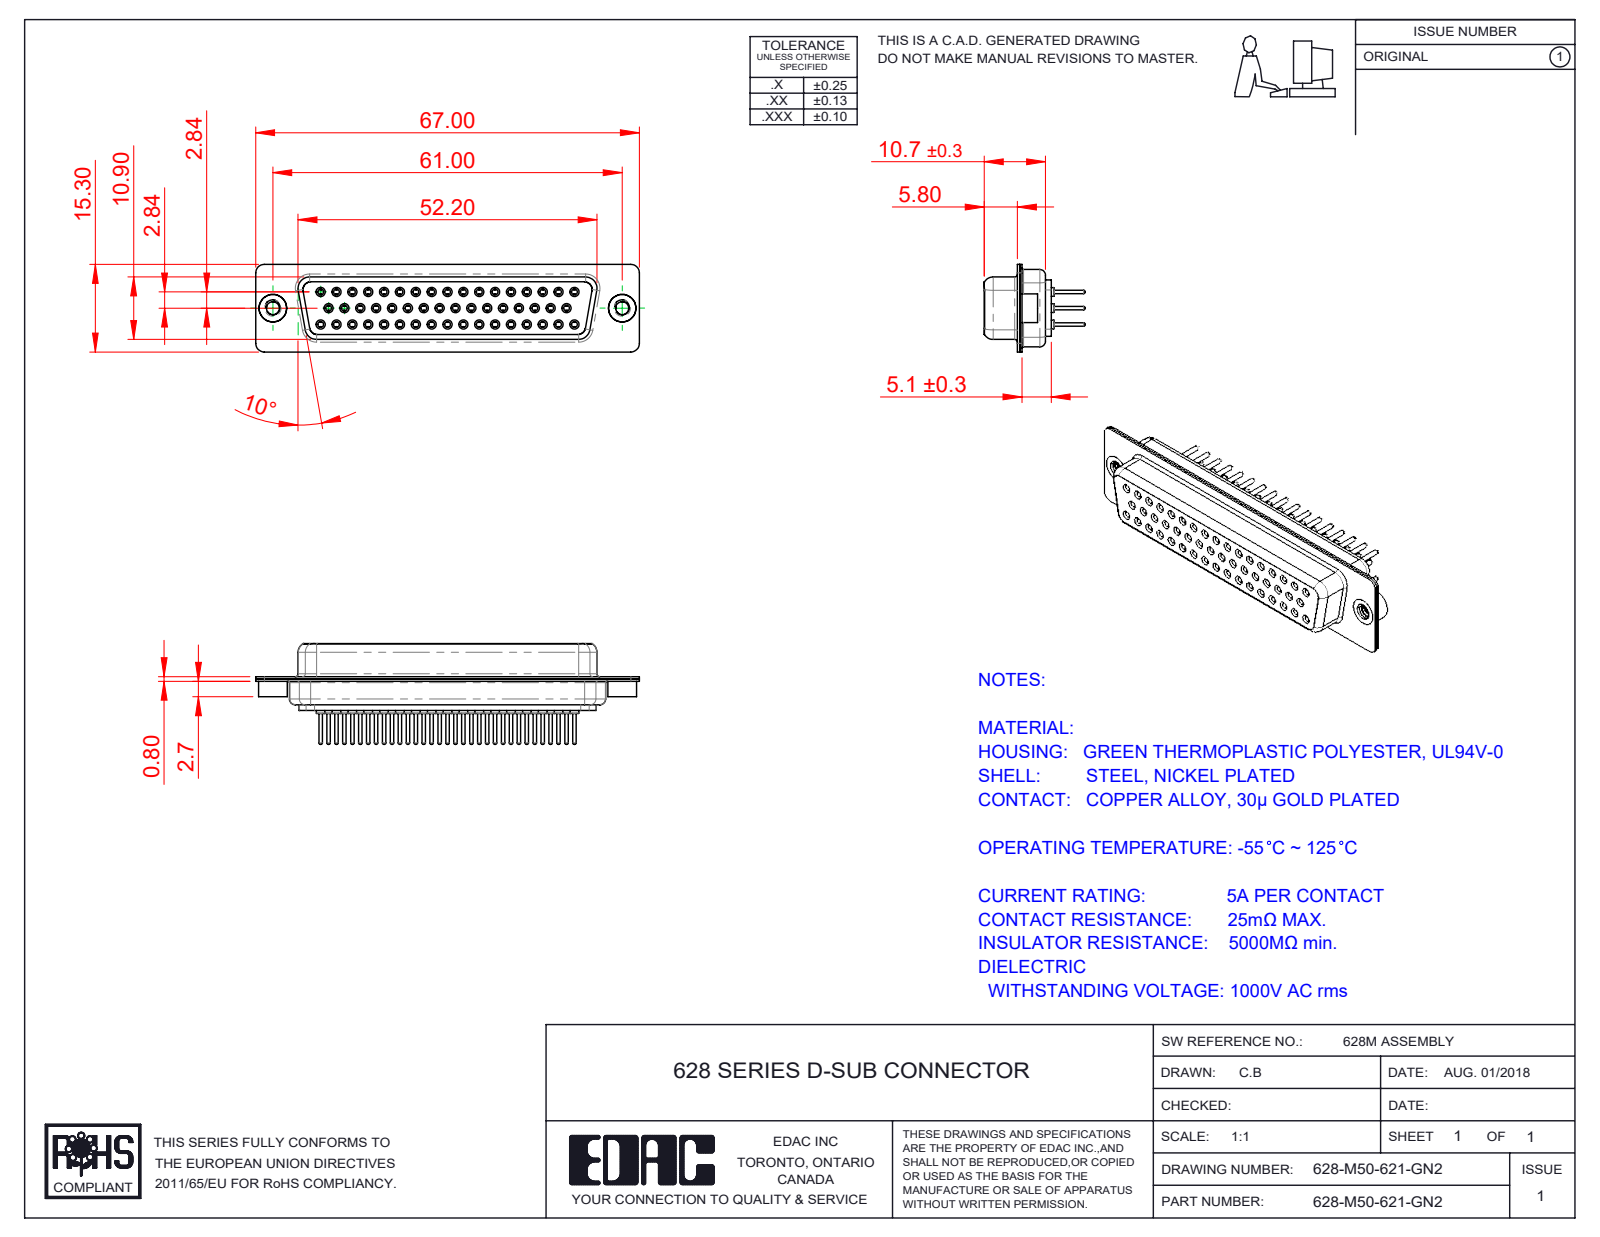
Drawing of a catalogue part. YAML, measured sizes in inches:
part_name: "628M Shell Front_50 Contacts; 628M Contact Row 2_21; 628M Contact Row 1_21; 628-M50-621-GN2 (+4 more)"
step_written_by: "SolidWorks 2020 (CONFIG_CONTROL_DESIGN)"
units: inches
bodies: {solids: 55, faces: 3029, planar: 817, cylindrical: 1087, other: 1125}
overall_size: [2.638, 0.693, 0.602]
volume: 0.404
surface_area: 23.32
round_holes:
  - {diameter: 0.039, count: 50}
  - {diameter: 0.043, count: 50}
  - {diameter: 0.067, count: 50}
  - {diameter: 0.071, count: 50}
  - {diameter: 0.079, count: 50}
  - {diameter: 0.089, count: 2}
  - {diameter: 0.157, count: 2}
  - {diameter: 0.189, count: 2}
round_bosses_or_shafts:
  - {diameter: 0.087, count: 50}
  - {diameter: 0.063, count: 50}
  - {diameter: 0.059, count: 50}
  - {diameter: 0.024, count: 50}
  - {diameter: 0.197, count: 2}
  - {diameter: 0.193, count: 2}
partial_cylinders:
  - {radius: 0.059, count: 16}
  - {radius: 0.079, count: 12}
  - {radius: 0.053, count: 8}
  - {radius: 0.063, count: 8}
  - {radius: 0.01, count: 4}
  - {radius: 0.02, count: 4}
  - {radius: 0.024, count: 4}
  - {radius: 0.026, count: 4}
face_to_face_distances: [0.016, 0.051, 0.465, 0.035, 0.217, 0.232, 0.033, 0.516, 0.228, 0.396]
hole_center_spacings: [0.124, 0.109, 0.218, 0.327, 0.436, 0.545, 0.654, 0.763]
